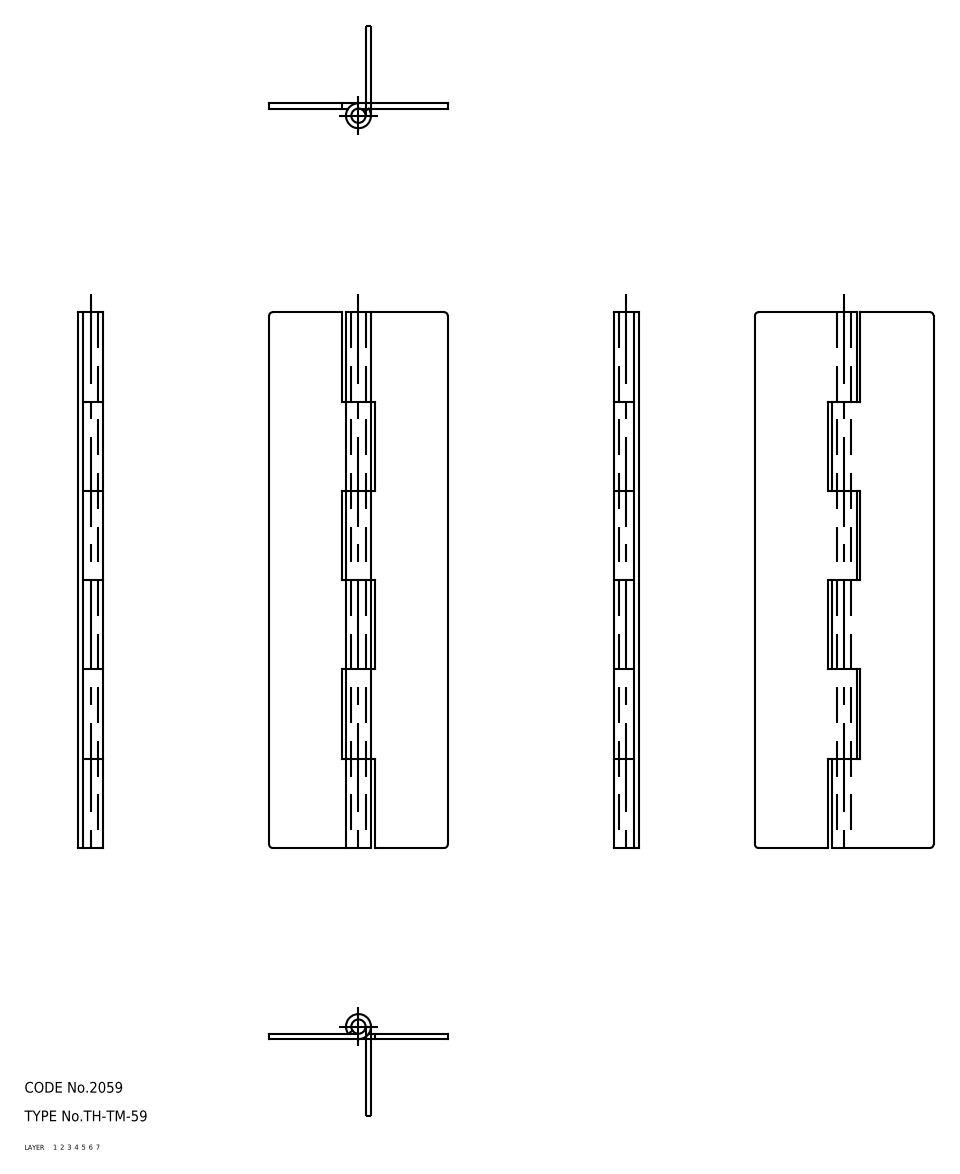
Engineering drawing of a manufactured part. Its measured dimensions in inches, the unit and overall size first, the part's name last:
Units: inches
Overall size (bounding box): 5.906 × 1.969 × 0.276
Volume: 0.94 in³ · Surface area: 33.01 in²
Bodies: 3 solids, 52 faces (0 planar, 0 cylindrical, 52 other)
Part name (STEP PRODUCT): hinge piece_B; hinge piece_A; shaft; TH_TM_59_24368_36
STEP written by: CADfix (AUTOMOTIVE_DESIGN)
